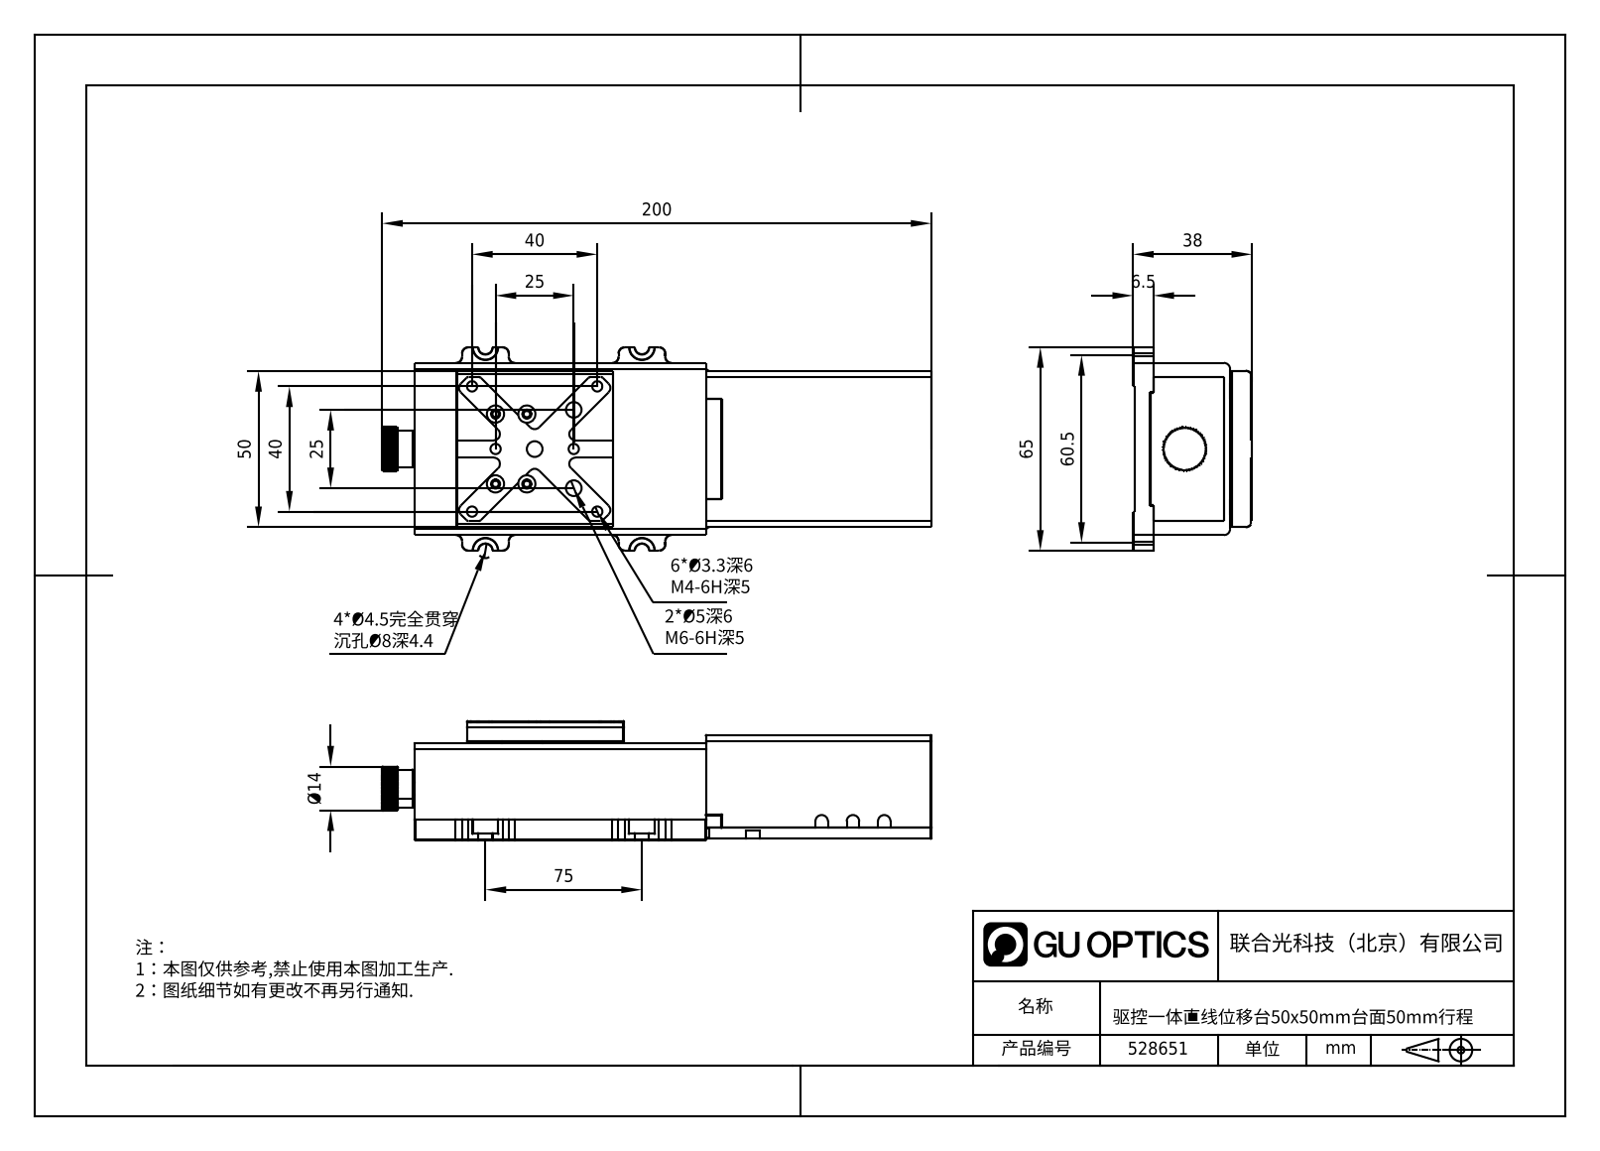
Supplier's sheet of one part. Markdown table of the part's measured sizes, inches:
| quantity | value |
| --- | --- |
| part name | 528651 |
| STEP written by | SolidWorks 2020 (CONFIG_CONTROL_DESIGN) |
| units | inches |
| bodies | 40 solids, 2836 faces (1645 planar, 783 cylindrical, 408 other) |
| overall size | 7.894 × 2.559 × 1.496 |
| volume | 13.23 in³ |
| surface area | 180.1 in² |
| round holes (diameter × count) | 0.094 × 24, 0.081 × 21, 0.114 × 18, 0.217 × 18, 0.142 × 12, 0.173 × 12, 0.062 × 10, 0.063 × 8, 0.079 × 8, 0.13 × 6, 0.197 × 4, 0.098 × 3 |
| round bosses / shafts (diameter × count) | 0.087 × 4, 0.079 × 4, 0.866 × 1, 0.512 × 1, 0.472 × 1, 0.118 × 1 |
| partial cylindrical surfaces (radius × count) | 0.079 × 41, 0.039 × 28, 0.004 × 16, 0.013 × 8, 0.009 × 6, 0.051 × 4, 0.087 × 4, 0.089 × 4 |
| main face-to-face distances | 0.098, 0.079, 0.157, 0.177, 0.039, 0.197, 1.201, 0.236, 0.059, 1.102 |
| hole center spacings | 0.591, 1.349, 0.278, 0.64, 0.906, 1.181, 1.213, 1.693 |
